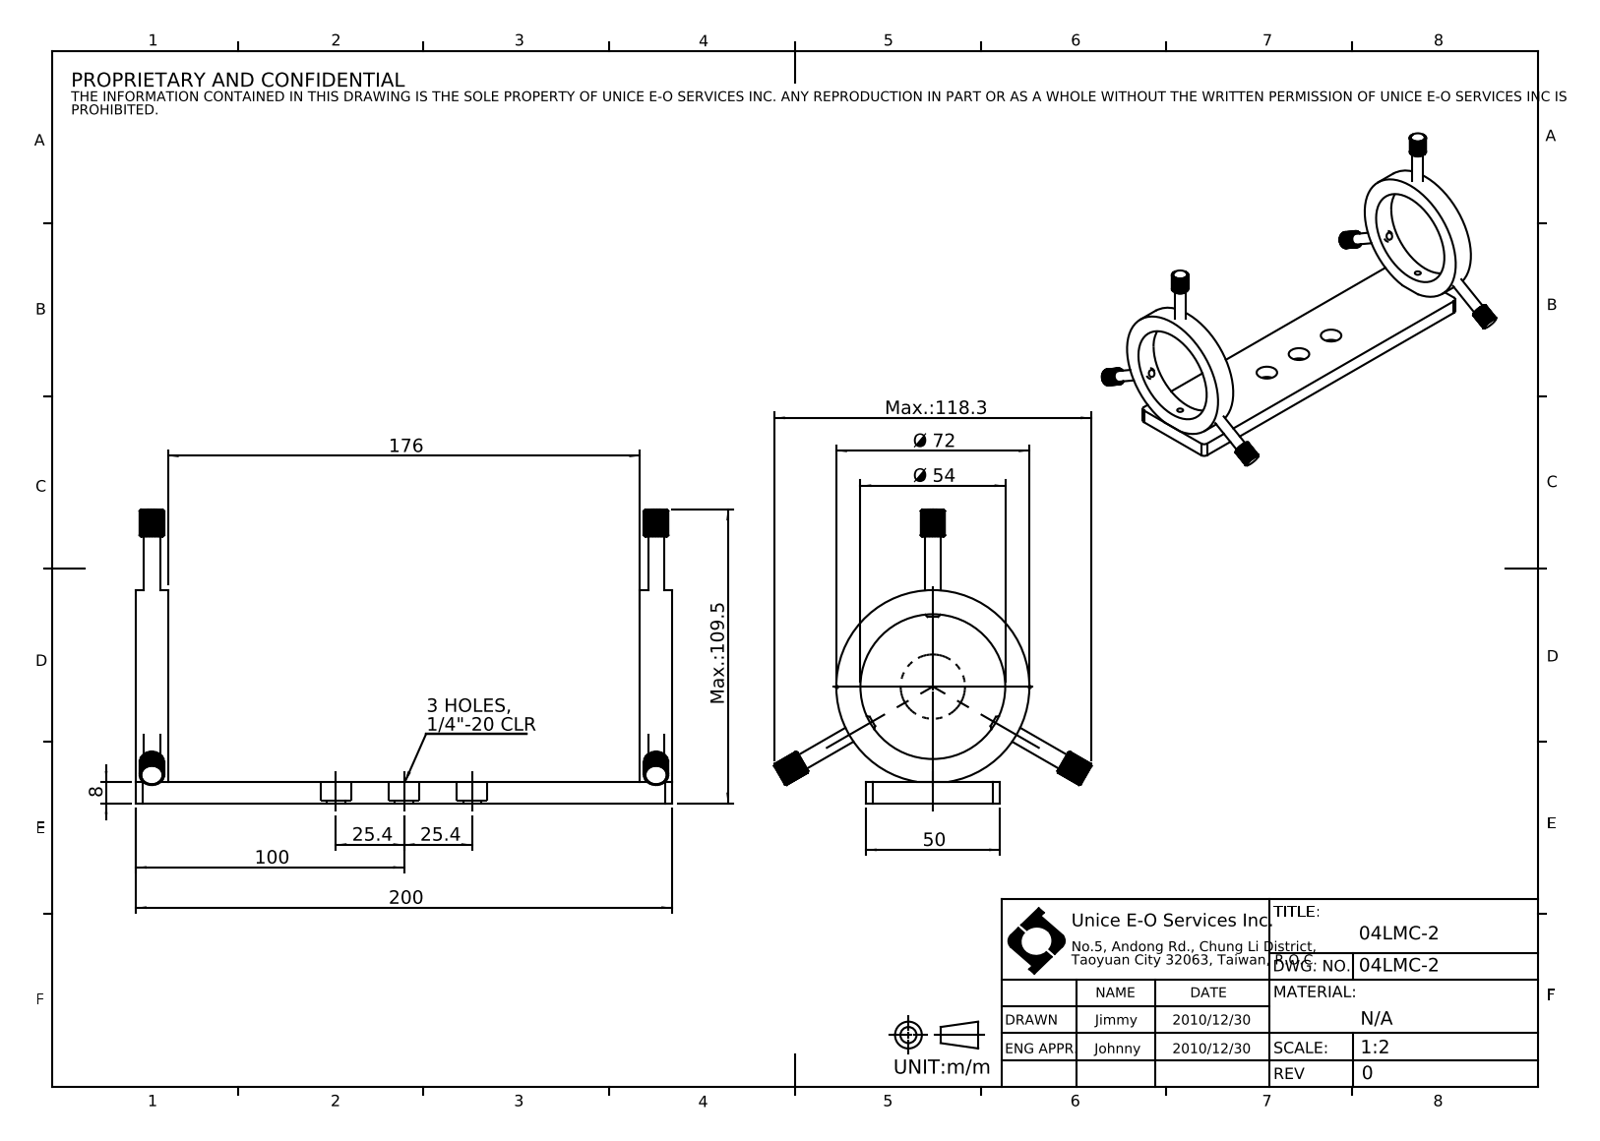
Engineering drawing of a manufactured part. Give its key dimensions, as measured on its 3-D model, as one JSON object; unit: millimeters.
{"part_name": "04LMC-2", "step_written_by": "SolidWorks 2016 (CONFIG_CONTROL_DESIGN)", "units": "millimeters", "bodies": {"solids": 9, "faces": 943, "planar": 575, "cylindrical": 332, "other": 36}, "overall_size": [200, 118.31, 109.5], "volume_mm3": 127122, "surface_area_mm2": 49108, "round_holes": [[5, 6], [6.76, 3], [11.51, 3], [3.3, 2], [4.5, 2], [8, 2], [54, 1]], "round_bosses_or_shafts": [[6, 6], [72, 1]], "partial_cylinders_radius": [[4.5, 6], [2.5, 4]], "face_to_face_distances": [8, 188, 12, 200, 176, 50, 7, 1, 10, 101.5], "hole_center_spacings": [188, 25.4, 68.6, 94, 119.4, 50.8]}
